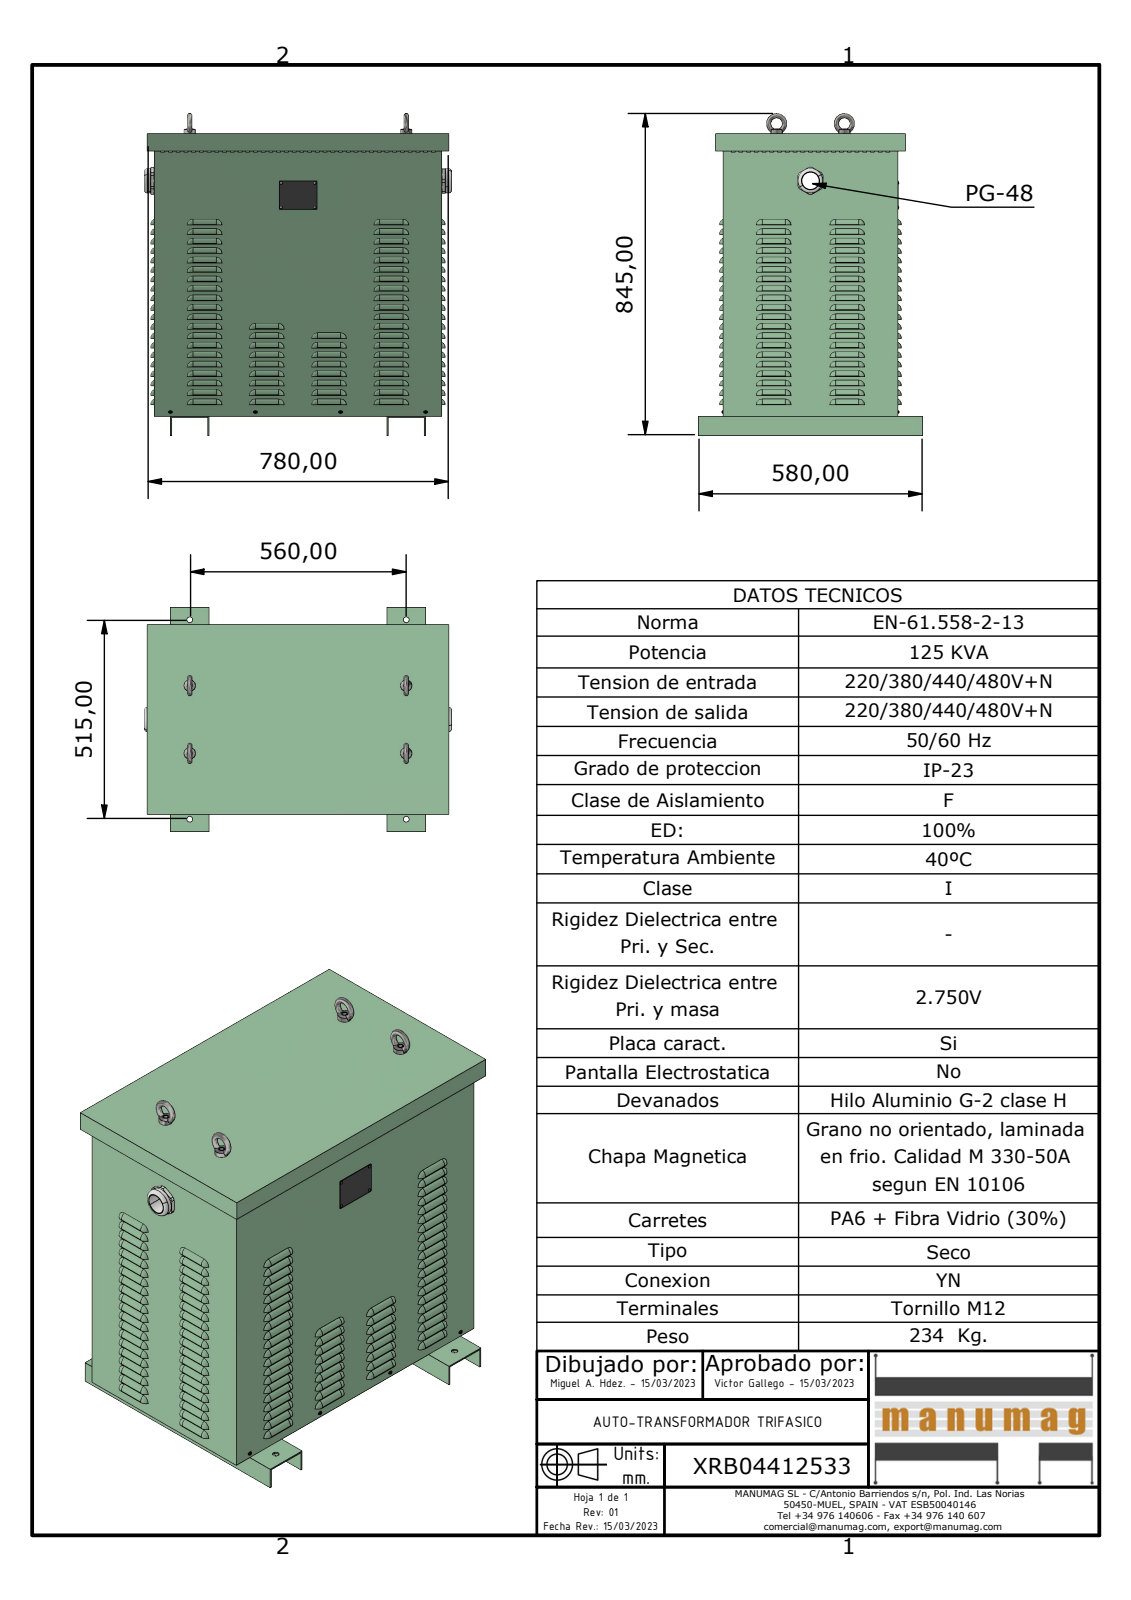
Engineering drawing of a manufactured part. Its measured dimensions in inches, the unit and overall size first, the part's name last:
Units: inches
Overall size (bounding box): 32.874 × 31.31 × 22.835
Round holes (diameter × count): ⌀0.433 ×780, ⌀0.591 ×8, ⌀0.157 ×4, ⌀0.197 ×4, ⌀0.398 ×4, ⌀1.732 ×1, ⌀2.362 ×1
Round bosses / shafts (diameter × count): ⌀1.181 ×4, ⌀0.157 ×4, ⌀0.143 ×4, ⌀0.126 ×4, ⌀2.48 ×1, ⌀2.335 ×1, ⌀2.329 ×1, ⌀2.269 ×1
Partial cylindrical surfaces — rounded edges, fillets, slot ends (radius × count): R0.551 ×194, R0.276 ×80, R0.591 ×80, R0.098 ×8, R0.079 ×4, R1.378 ×1
Main face-to-face distances: 0.079, 17.717, 28.74, 29.213, 17.638, 17.795, 28.819, 29.134, 28.661, 29.291
Hole centre spacings: 0.819, 6.481, 1.31, 5.893, 7.047, 1.181, 1.86, 5.866
Volume: 407.2 in³ · Surface area: 9 164 in²
Bodies: 24 solids, 4123 faces (1445 planar, 1686 cylindrical, 992 other)
Part name (STEP PRODUCT): XRB04412533; JE125 - JE160NACIONAL CUERPO; JE125 JE160 NACIONAL BASE; JE125 - JE160 NACIONAL PATA (+6 more)
STEP written by: Autodesk Inventor 2023 (AUTOMOTIVE_DESIGN)
